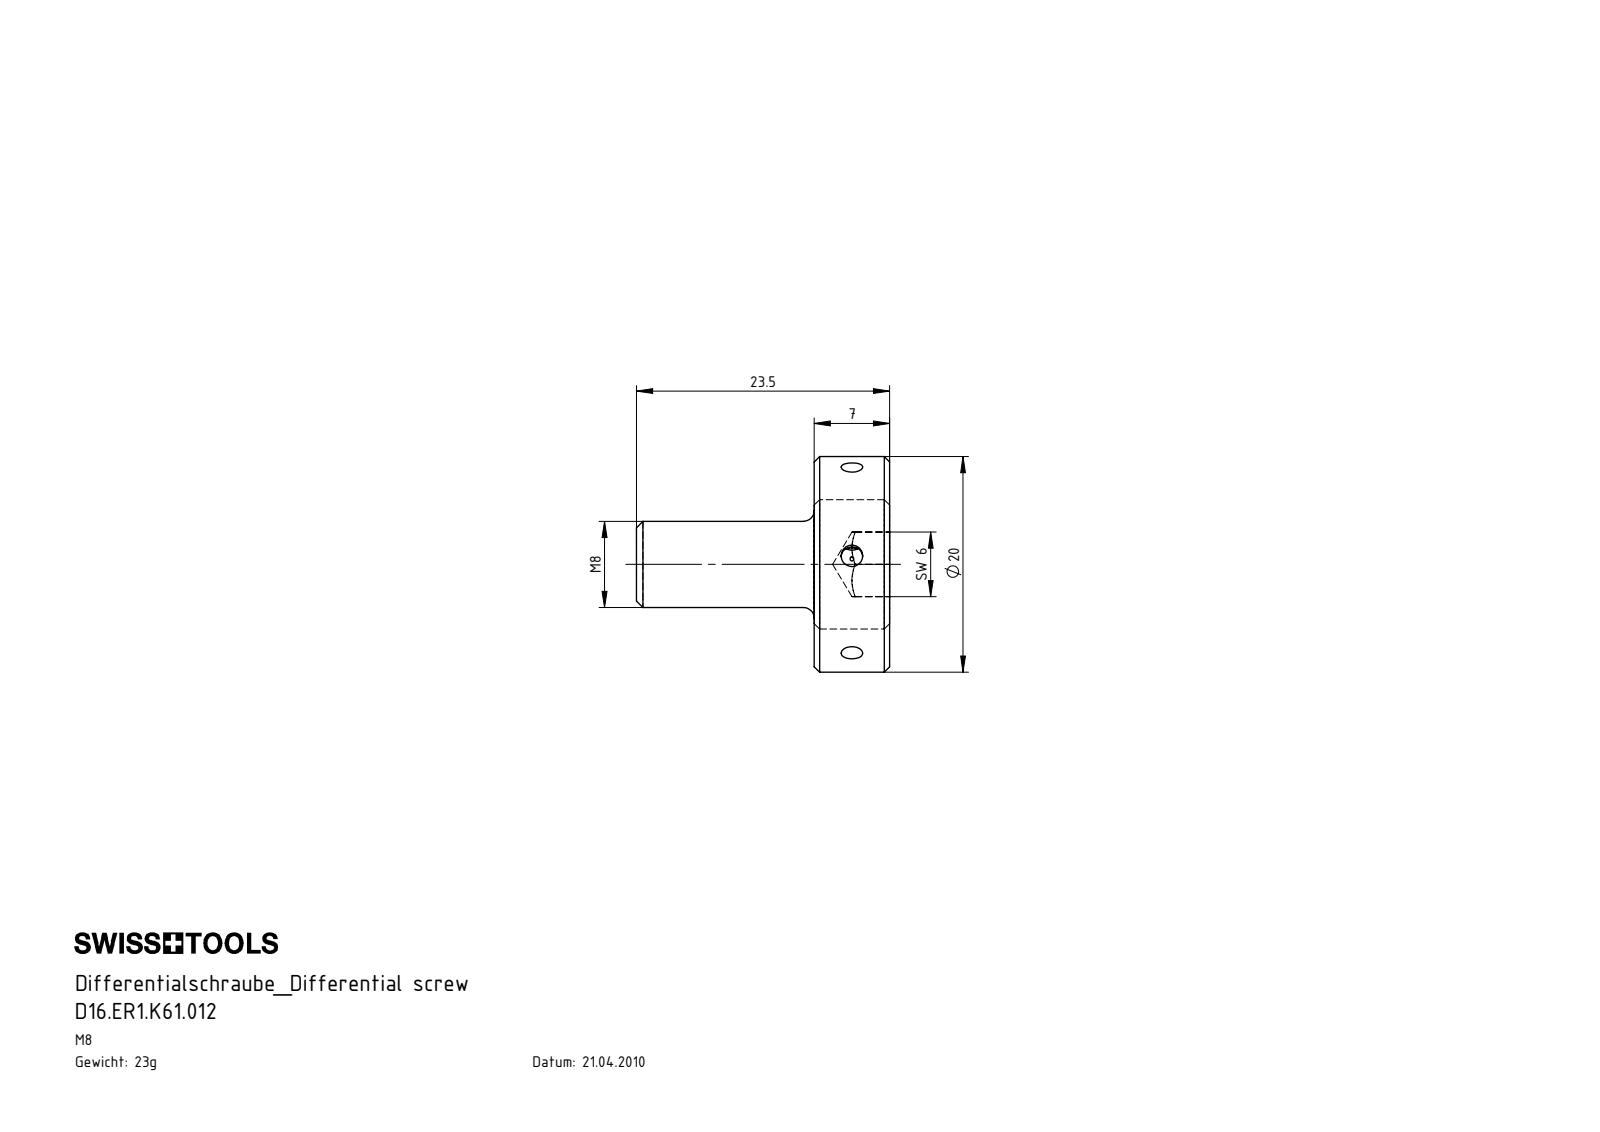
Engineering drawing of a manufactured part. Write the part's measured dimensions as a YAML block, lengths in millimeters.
part_name: "D16-ER1.K61.012; D16-ER1.K62.007_A; D16-ER1.K63.012_A"
step_written_by: "SolidWorks 2012 (AUTOMOTIVE_DESIGN)"
units: millimeters
bodies: {solids: 2, faces: 129, planar: 11, cylindrical: 58, other: 60}
overall_size: [23.5, 20, 20]
volume: 2877
surface_area: 2201
round_holes:
  - {diameter: 2, count: 10}
  - {diameter: 11, count: 1}
round_bosses_or_shafts:
  - {diameter: 20, count: 1}
  - {diameter: 12, count: 1}
  - {diameter: 8, count: 1}
face_to_face_distances: [7, 16.5, 23.5, 6]
hole_center_spacings: [7.5, 12.99, 7.51, 13, 15.01, 14.99]
